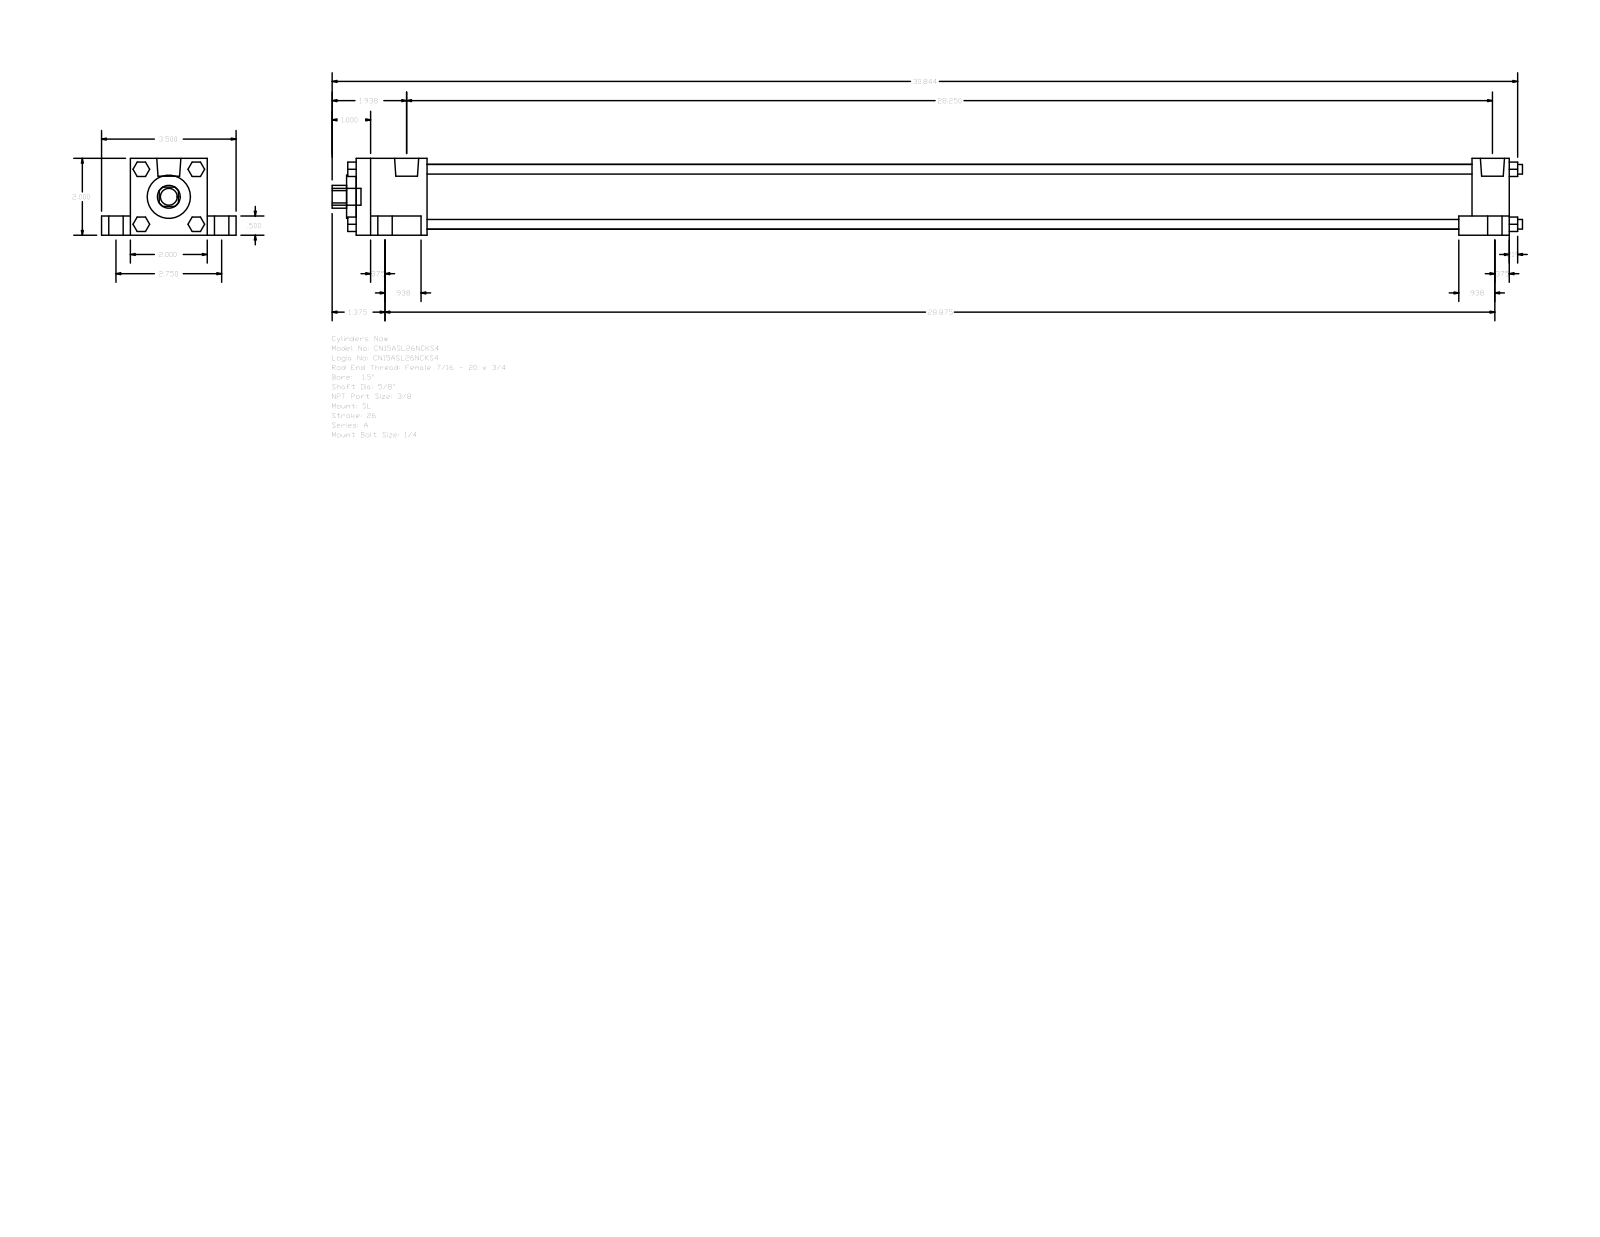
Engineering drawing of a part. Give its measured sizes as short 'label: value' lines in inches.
name: A_SL__0150_0.625
written by: GSSL Pune (CONFIG_CONTROL_DESIGN)
unit: in
bodies: 0 solids, 148 faces (112 planar, 36 cylindrical, 0 other)
size: 30.969 × 3.5 × 2
holes: 1× ⌀0.625, 1× ⌀1.125, 1× ⌀1.69
bosses: 4× ⌀0.625, 4× ⌀0.375, 4× ⌀0.25, 4× ⌀0.219, 2× ⌀0.627, 1× ⌀0.437
rounds: 1× R0.297
face distances: 2, 0.75, 0.5, 1.5, 2.75, 30, 0.375, 1.313, 29.031, 0.969
